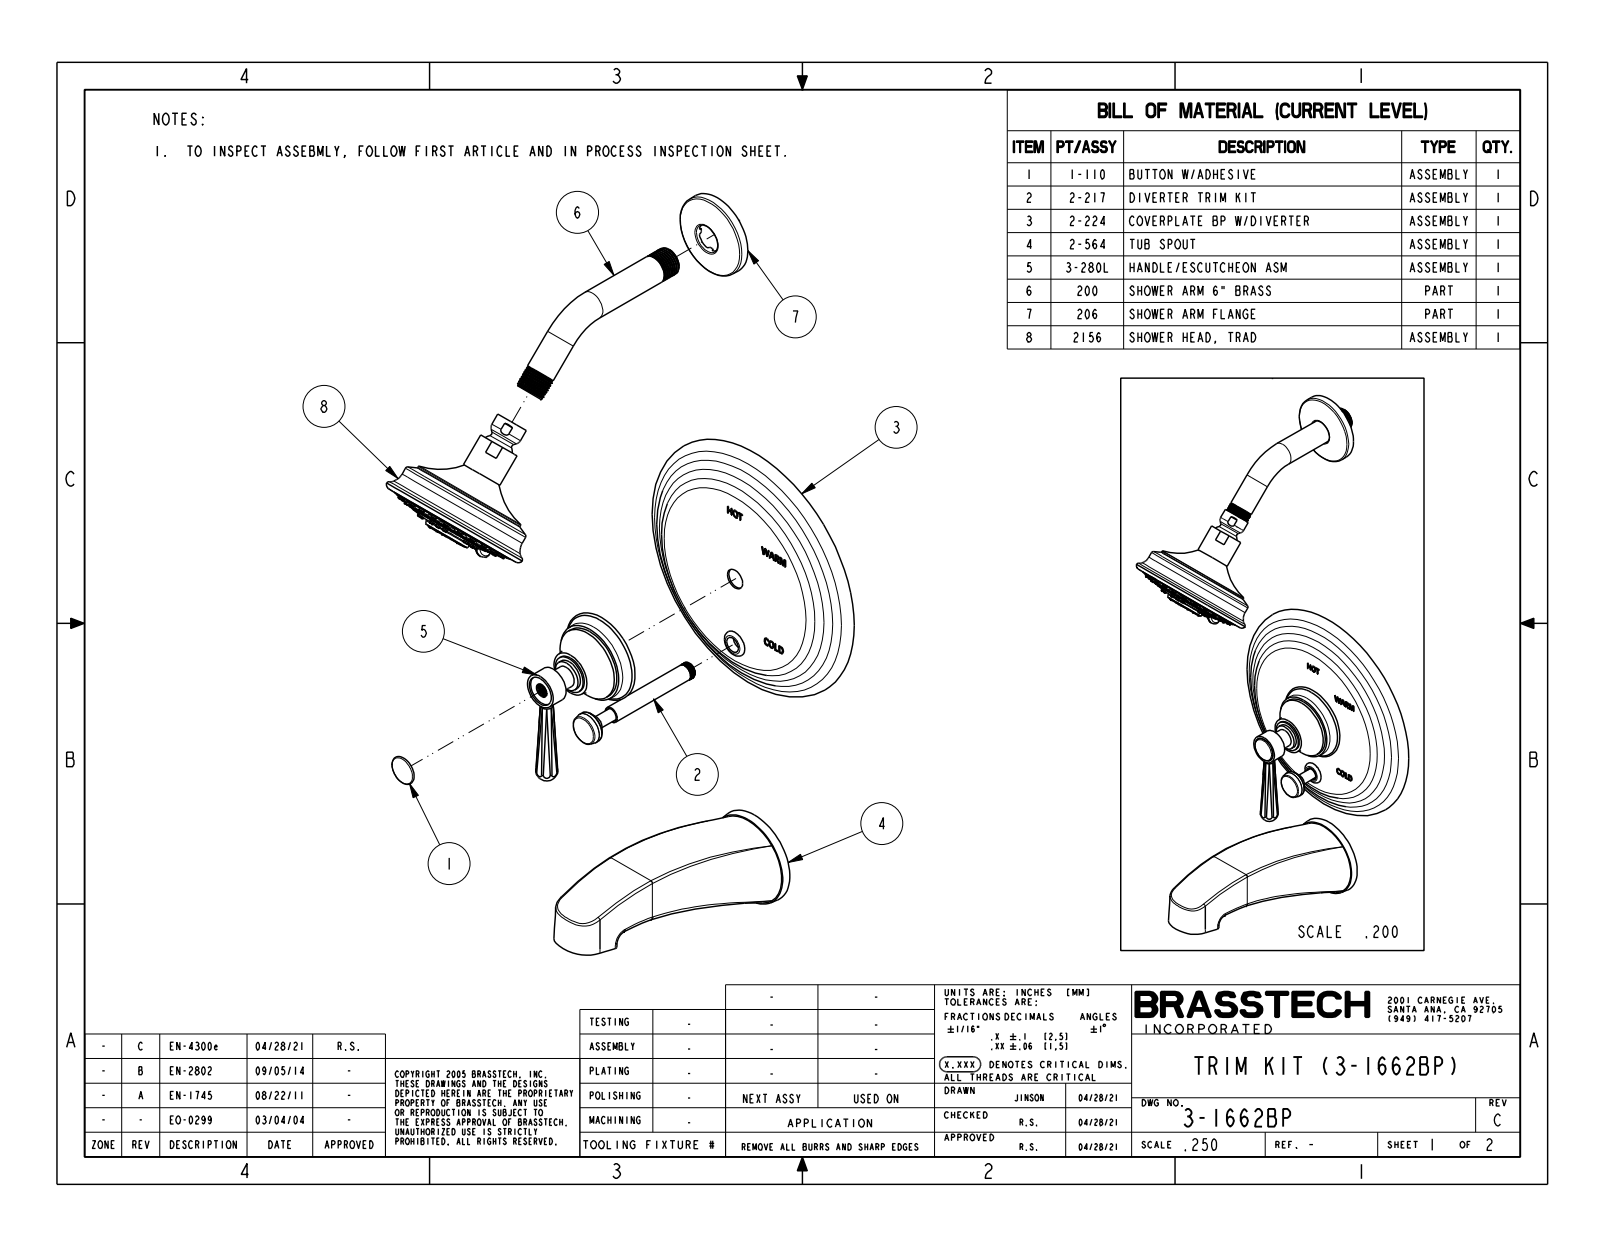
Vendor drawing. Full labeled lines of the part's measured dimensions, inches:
Part name (STEP PRODUCT): 3-1662BP
STEP written by: CREO PARAMETRIC BY PTC INC, 2018400 (CONFIG_CONTROL_DESIGN)
Units: inches
Bodies: 3 solids, 1344 faces (252 planar, 216 cylindrical, 876 other)
Overall size (bounding box): 20.565 × 8.25 × 7.75
Volume: 75.47 in³ · Surface area: 249.9 in²
Round holes (diameter × count): ⌀0.059 ×8, ⌀0.363 ×1, ⌀0.85 ×1, ⌀0.925 ×1
Round bosses / shafts (diameter × count): ⌀0.142 ×39, ⌀0.165 ×23, ⌀0.813 ×2, ⌀3.81 ×1, ⌀3.724 ×1, ⌀3.24 ×1, ⌀2.38 ×1, ⌀2.323 ×1
Partial cylindrical surfaces — rounded edges, fillets, slot ends (radius × count): R0.079 ×8, R0.02 ×2, R0.138 ×1, R0.472 ×1, R0.512 ×1, R0.63 ×1
Main face-to-face distances: 0.754, 0.063, 0.118, 0.181, 1.229, 0.475, 2.129, 1.375, 0.9, 1.167
Hole centre spacings: 0.443, 0.579, 0.818, 0.819, 1.069, 0.443, 0.578, 1.069
